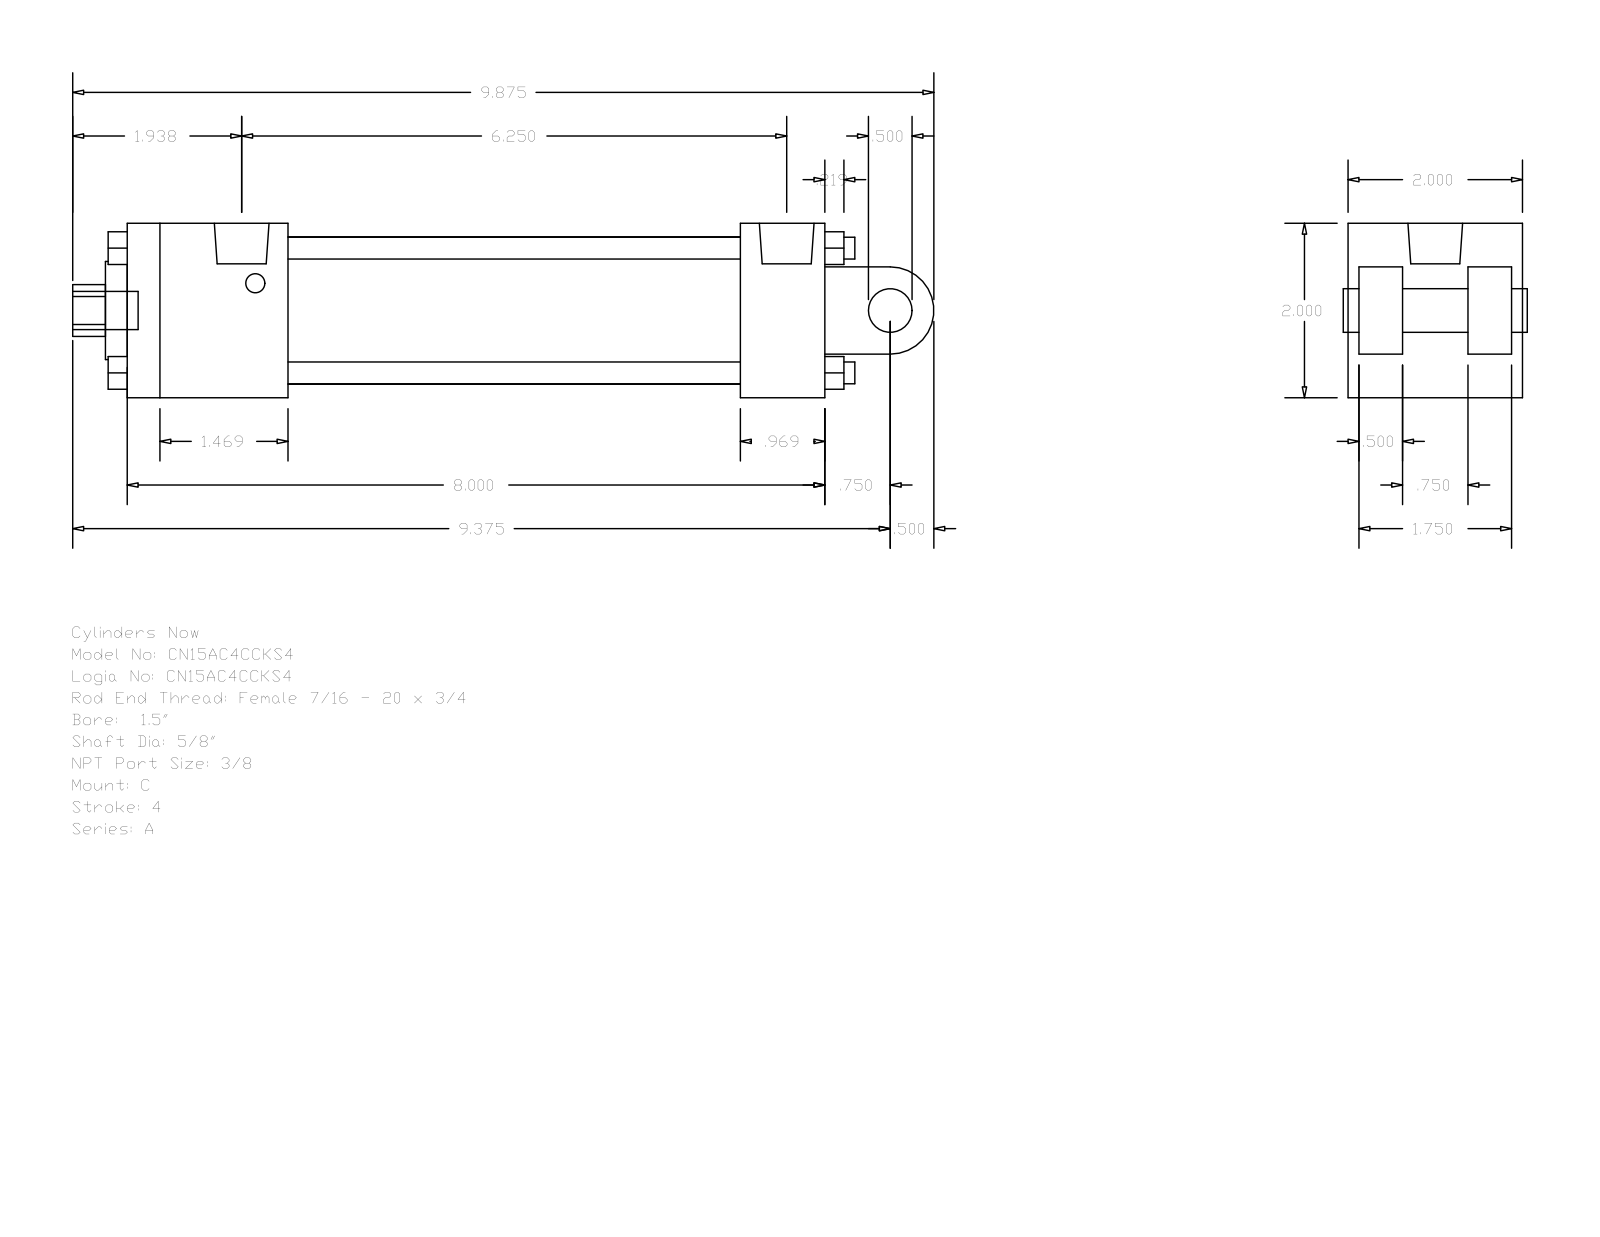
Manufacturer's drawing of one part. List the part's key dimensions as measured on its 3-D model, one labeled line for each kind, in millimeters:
Part name (STEP PRODUCT): A_C__0150_0.625
STEP written by: GSSL Pune (CONFIG_CONTROL_DESIGN)
Units: millimetres
Bodies: 0 solids, 135 faces (102 planar, 33 cylindrical, 0 other)
Overall size (bounding box): 250.82 × 50.8 × 50.8
Round holes (diameter × count): ⌀5.56 ×2, ⌀15.88 ×1, ⌀15.93 ×1, ⌀28.57 ×1, ⌀42.93 ×1
Round bosses / shafts (diameter × count): ⌀6.35 ×4, ⌀5.56 ×2, ⌀15.93 ×1, ⌀12.7 ×1, ⌀11.11 ×1
Partial cylindrical surfaces — rounded edges, fillets, slot ends (radius × count): R7.54 ×1, R12.7 ×1
Main face-to-face distances: 50.8, 12.7, 203.19, 3.17, 47.63, 15.87, 34.93, 31.76, 178.59, 24.6
Hole centre spacings: 3.97
